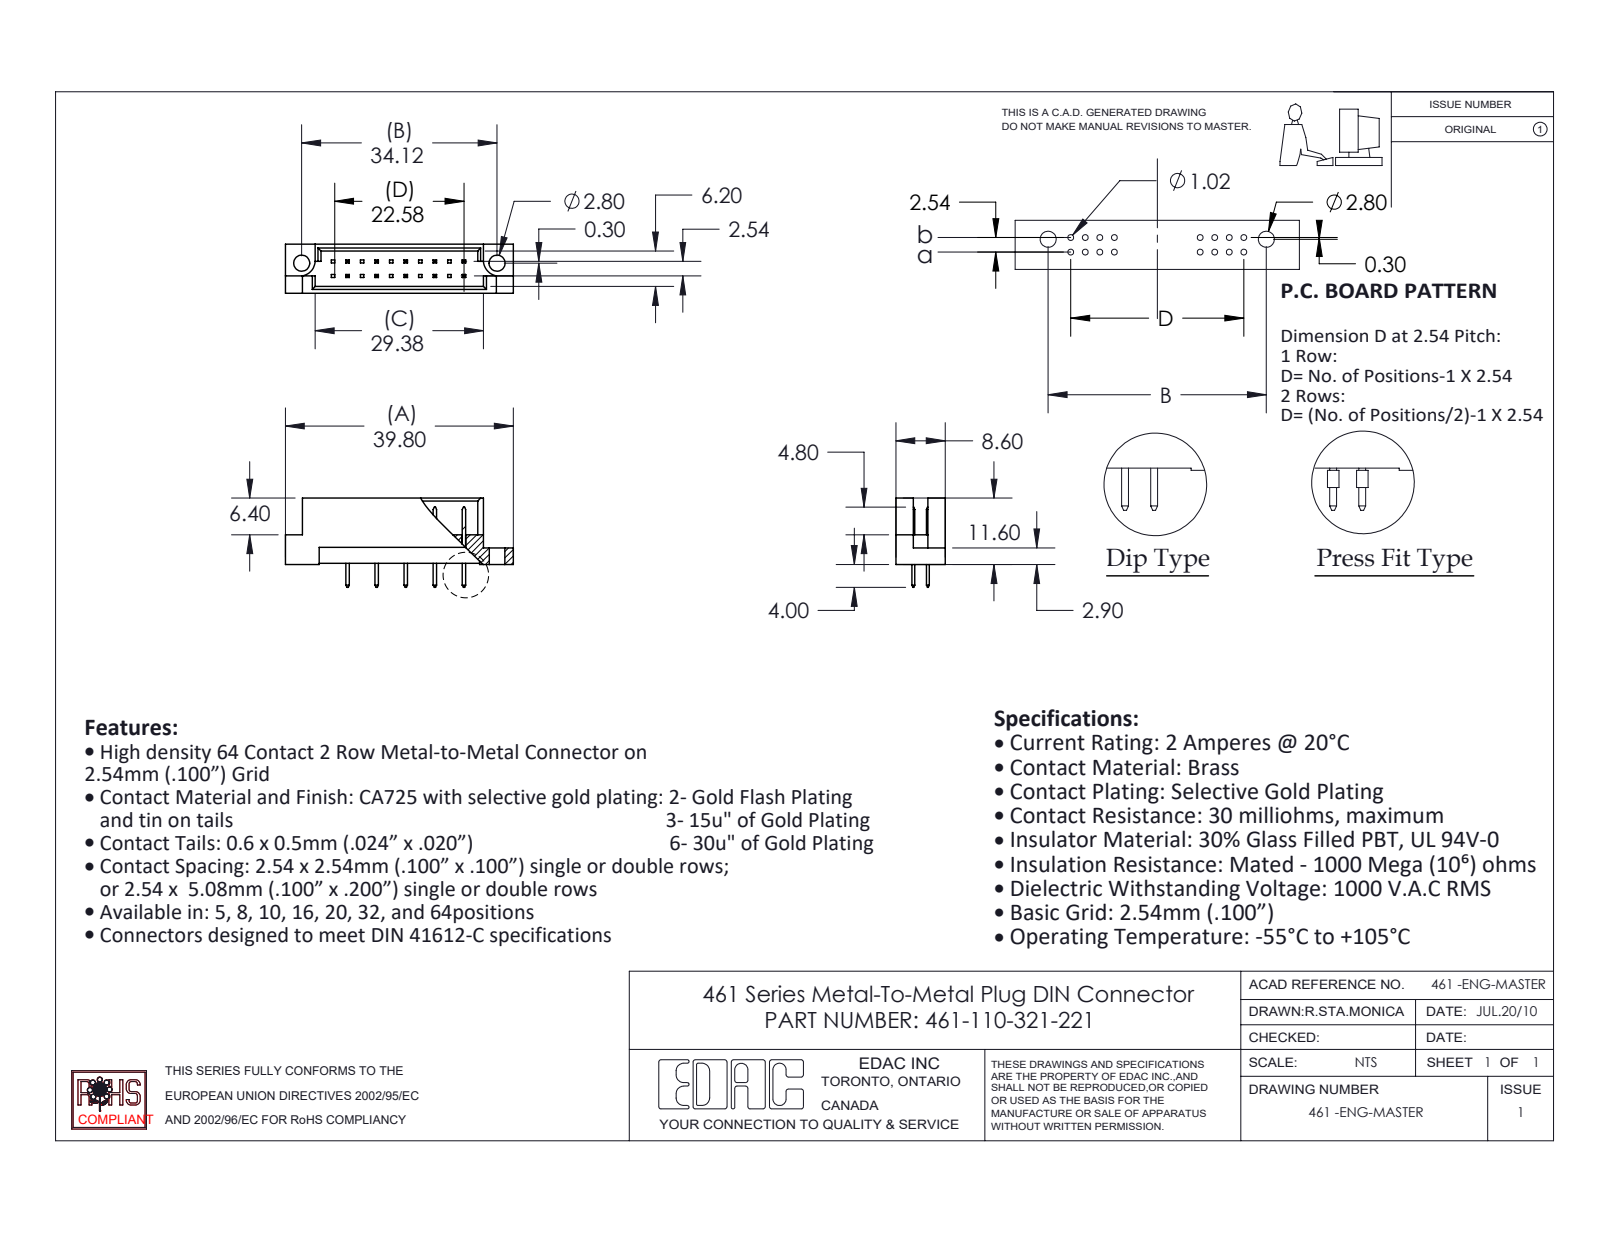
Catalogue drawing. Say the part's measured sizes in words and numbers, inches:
The part is named "461 Part_20; 461-290_21; 461-110-321-221". Its 3-D file was written by "SolidWorks 2020 (CONFIG_CONTROL_DESIGN)". It is 11 solids with 268 faces: 262 planar, 6 cylindrical and 0 other. Overall it measures 1.567 by 0.614 by 0.339 inches. Its volume is 0.119 cubic inches and its surface area 4.095 square inches. Round holes: 2 of diameter 0.11. Partial cylindrical surfaces (rounded edges, fillets, slot ends): 2 of radius 0.11. The main face-to-face distances are 0.047, 0.291, 0.339, 0.244, 0.197, 0.1, 0.2, 0.129, 0.209, 0.082. The hole center spacings are 1.343.
